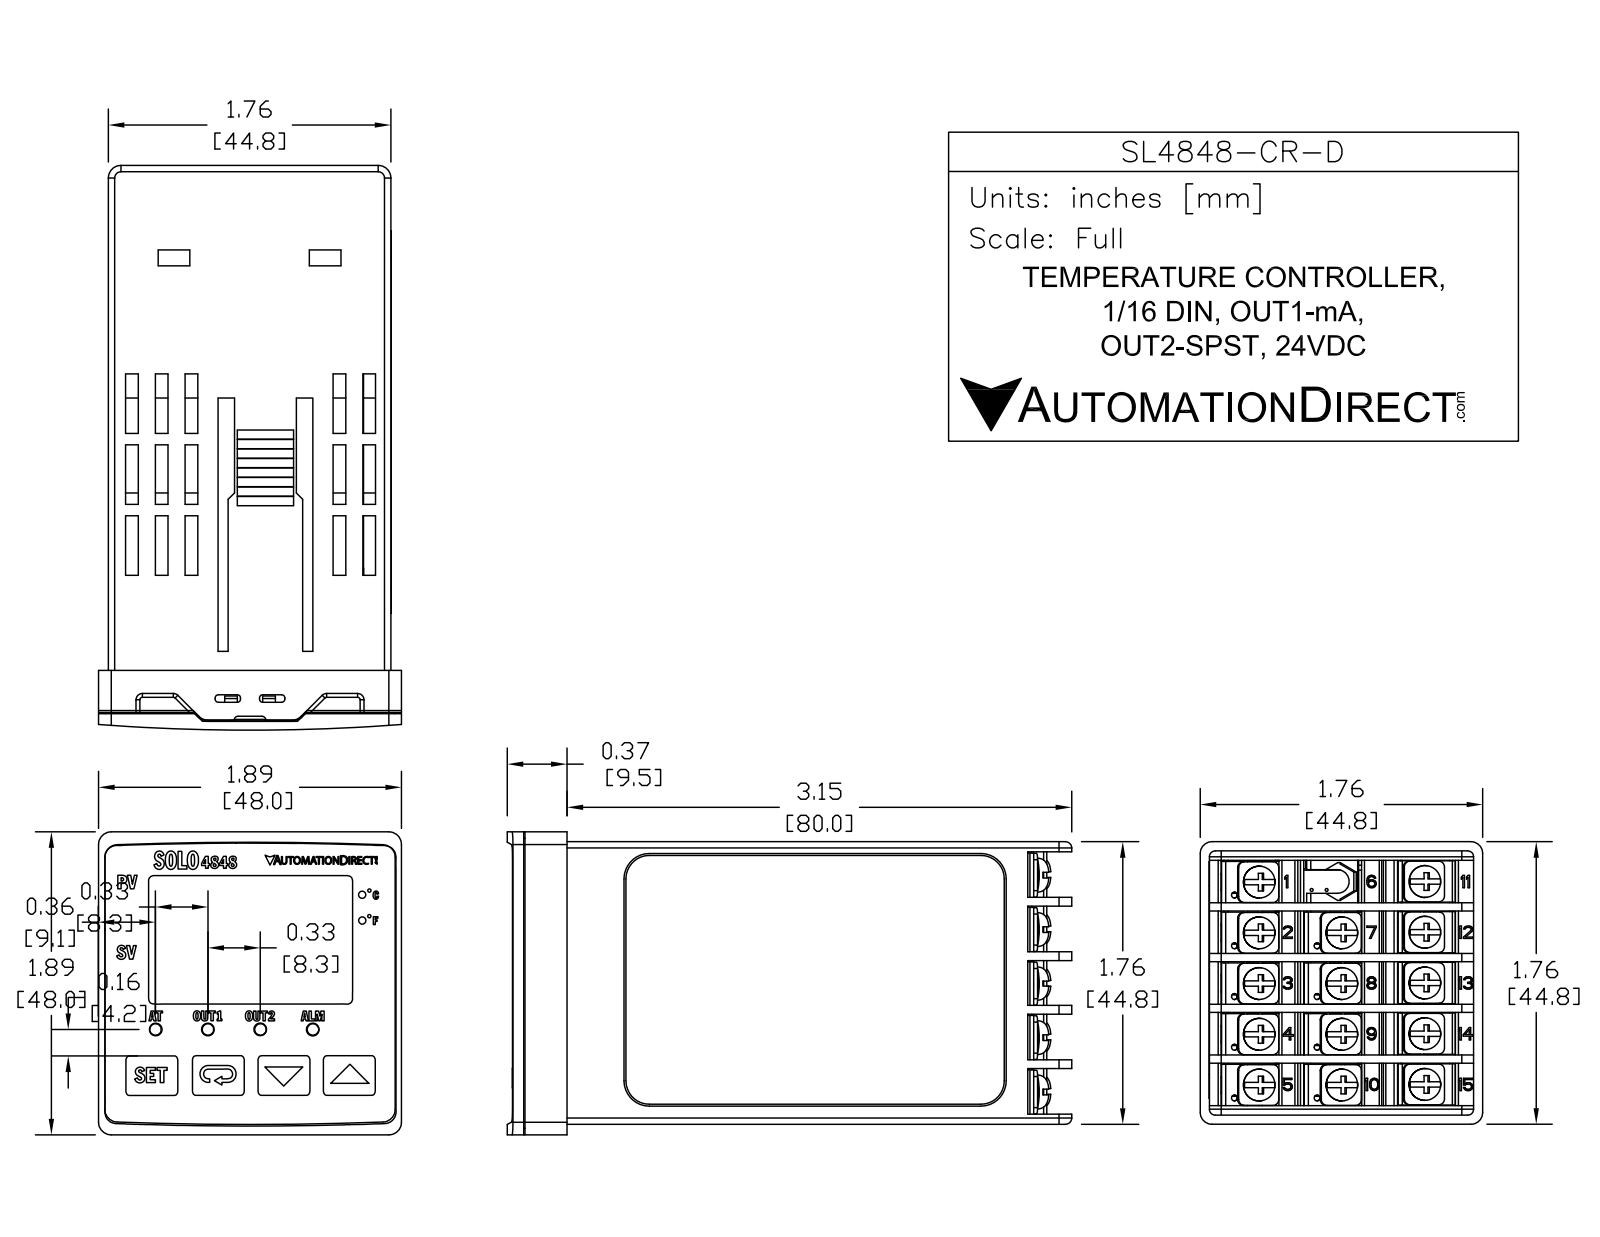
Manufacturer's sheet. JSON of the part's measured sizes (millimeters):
{"part_name": "SL4848-CR-D", "step_written_by": "SolidWorks 2011 (AUTOMOTIVE_DESIGN)", "units": "millimeters", "bodies": {"solids": 1, "faces": 1168, "planar": 799, "cylindrical": 174, "other": 195}, "overall_size": [89.4, 48.8, 48.8], "volume_mm3": 167800, "surface_area_mm2": 33170, "round_bosses_or_shafts": [[6.5, 15]], "partial_cylinders_radius": [[0.8, 70], [0.4, 12], [1, 8], [1, 4], [1.5, 4], [2, 4], [0.6, 2], [0.6, 2]], "face_to_face_distances": [44.7, 44.7, 1.5, 8.7, 1.7, 46.4, 17.4, 26.1, 15.8, 0.4]}
